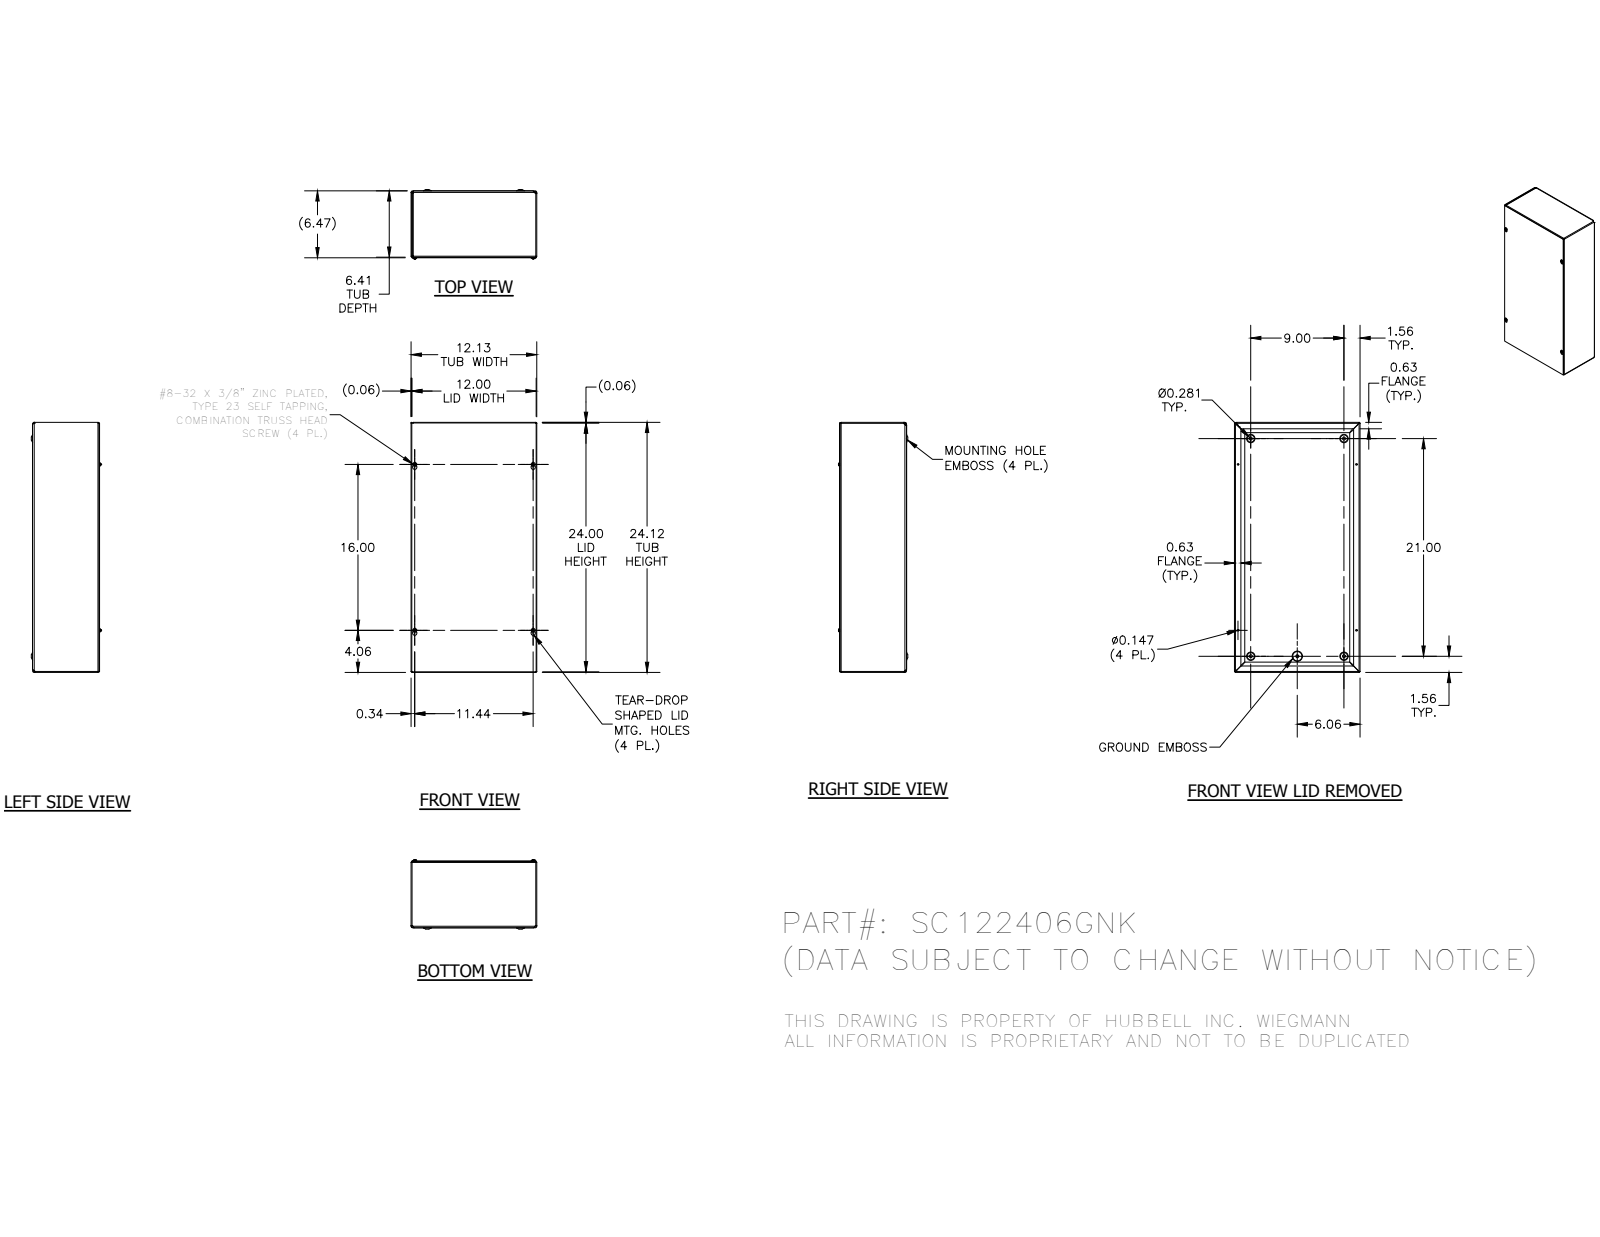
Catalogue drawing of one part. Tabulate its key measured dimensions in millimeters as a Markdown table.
| quantity | value |
| --- | --- |
| part name | SC1224GNKBKP; SC122406GNKWRA; SC1224GNKLID; 34056 (+1 more) |
| STEP written by | Autodesk Inventor 2014 (AUTOMOTIVE_DESIGN) |
| units | millimeters |
| bodies | 7 solids, 358 faces (133 planar, 73 cylindrical, 152 other) |
| overall size | 612.77 × 307.98 × 170 |
| volume | 1 147 000 mm³ |
| surface area | 1 467 000 mm² |
| round holes (diameter × count) | 3.73 × 4, 7.62 × 4, 4.19 × 1 |
| round bosses / shafts (diameter × count) | 9.75 × 4, 4.17 × 4, 5.8 × 1 |
| partial cylindrical surfaces (radius × count) | 0.79 × 8, 2.37 × 8, 1.4 × 4, 1.57 × 4, 2.38 × 4, 2.97 × 4, 3.15 × 4, 3.17 × 4 |
| main face-to-face distances | 1.57, 161.12, 162.69, 1.59, 162.71, 164.28, 1.58, 307.98, 306.41, 306.4 |
| hole center spacings | 70.66, 114.3, 228.6, 267.21, 290.51, 406.4, 470.9, 470.94 |
